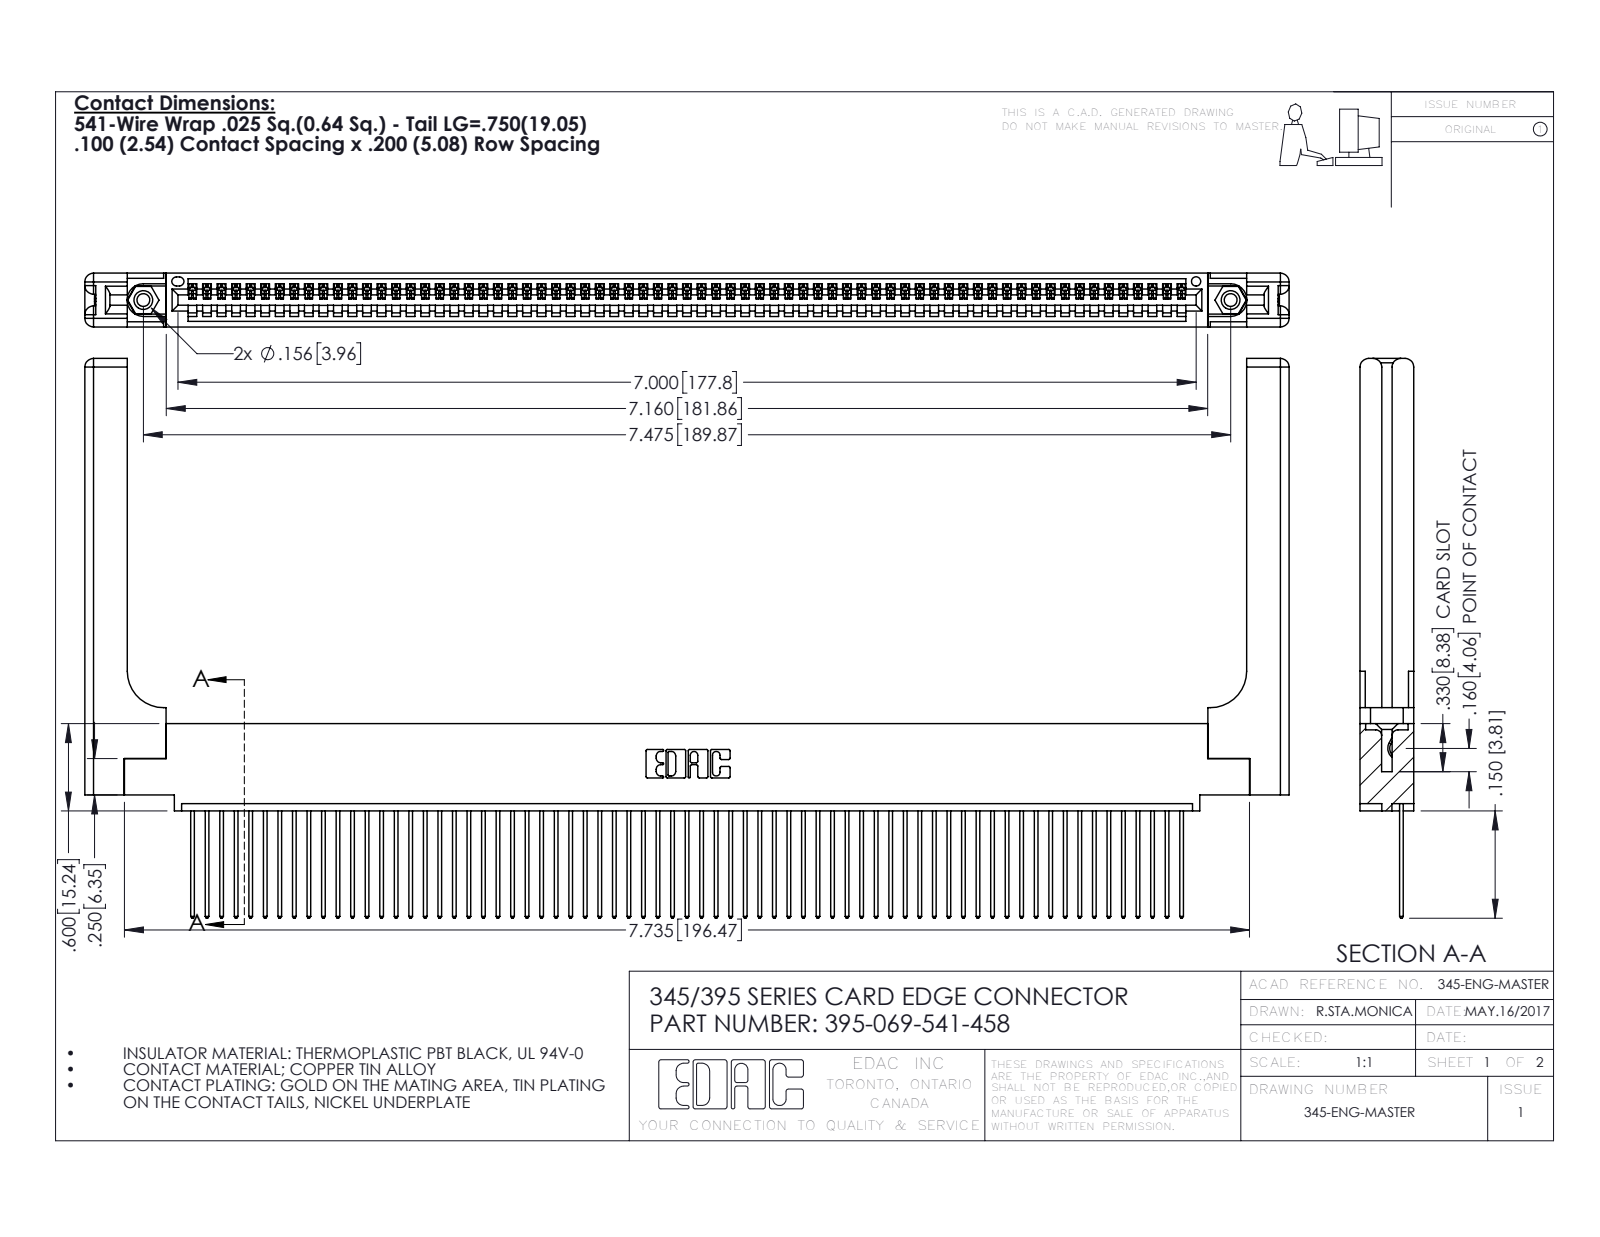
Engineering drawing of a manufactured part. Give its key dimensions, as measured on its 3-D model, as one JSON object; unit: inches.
{"part_name": "395-069-541-458; 345-220-058_345-220-058; 345-250-001_345-250-001-102; 345-292-001_345-293-141 (+1 more)", "step_written_by": "SolidWorks 2016 (CONFIG_CONTROL_DESIGN)", "units": "inches", "bodies": {"solids": 74, "faces": 4388, "planar": 2992, "cylindrical": 1336, "other": 60}, "overall_size": [8.279, 3.847, 0.37], "volume_in3": 1.761, "surface_area_in2": 52.91, "round_holes": [[0.089, 2], [0.125, 2], [0.156, 2], [0.064, 1]], "round_bosses_or_shafts": [[0.155, 2]], "partial_cylinders_radius": [[0.006, 138], [0.01, 138], [0.01, 22], [0.06, 16], [0.007, 6], [0.031, 6], [0.026, 3], [0.03, 2]], "face_to_face_distances": [0.072, 0.298, 0.37, 0.098, 0.272, 0.025, 0.2, 0.225, 0.148, 0.15], "hole_center_spacings": [0.27, 7.239, 7.475]}
